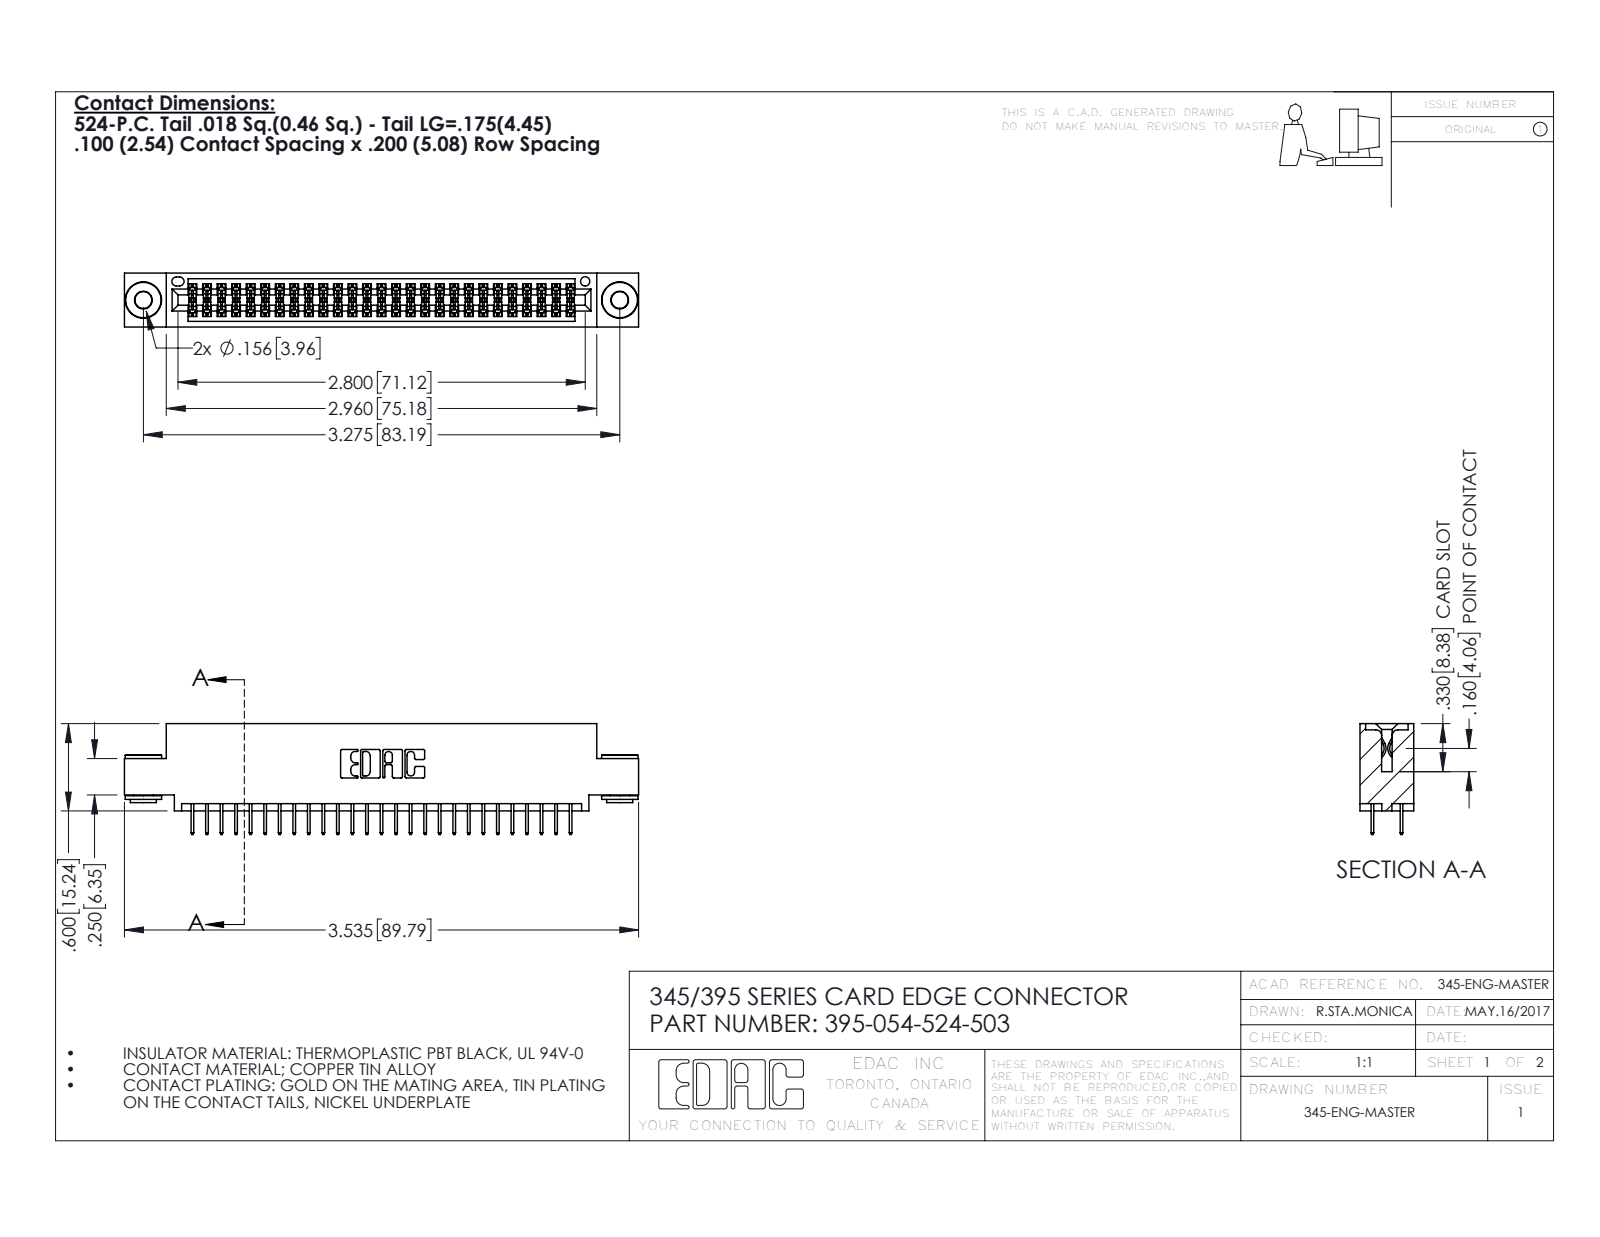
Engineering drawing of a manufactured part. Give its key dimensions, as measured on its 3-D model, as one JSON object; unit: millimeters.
{"part_name": "345 Part_0.110 Offset - 0.156 Dia-TH; 345-292-001_345-293-124; 345-250-002_345-250-002-102; 395-054-524-503", "step_written_by": "SolidWorks 2016 (CONFIG_CONTROL_DESIGN)", "units": "millimeters", "bodies": {"solids": 57, "faces": 3084, "planar": 2200, "cylindrical": 876, "other": 8}, "overall_size": [89.8, 19.4, 9.4], "volume_mm3": 8440, "surface_area_mm2": 12280, "round_holes": [[2.9, 2], [4, 2], [1.6, 1]], "round_bosses_or_shafts": [[6.4, 2], [4.6, 2], [3.5, 2]], "partial_cylinders_radius": [[0.2, 81], [0.3, 22], [0.2, 6], [0.8, 6], [0.7, 3], [0.4, 2], [0.5, 2], [0.6, 2]], "face_to_face_distances": [1.8, 7.6, 5.1, 9.4, 0.6, 2.5, 6.9, 5.7, 1.8, 4.4], "hole_center_spacings": [6.9, 77.2, 83.2]}
